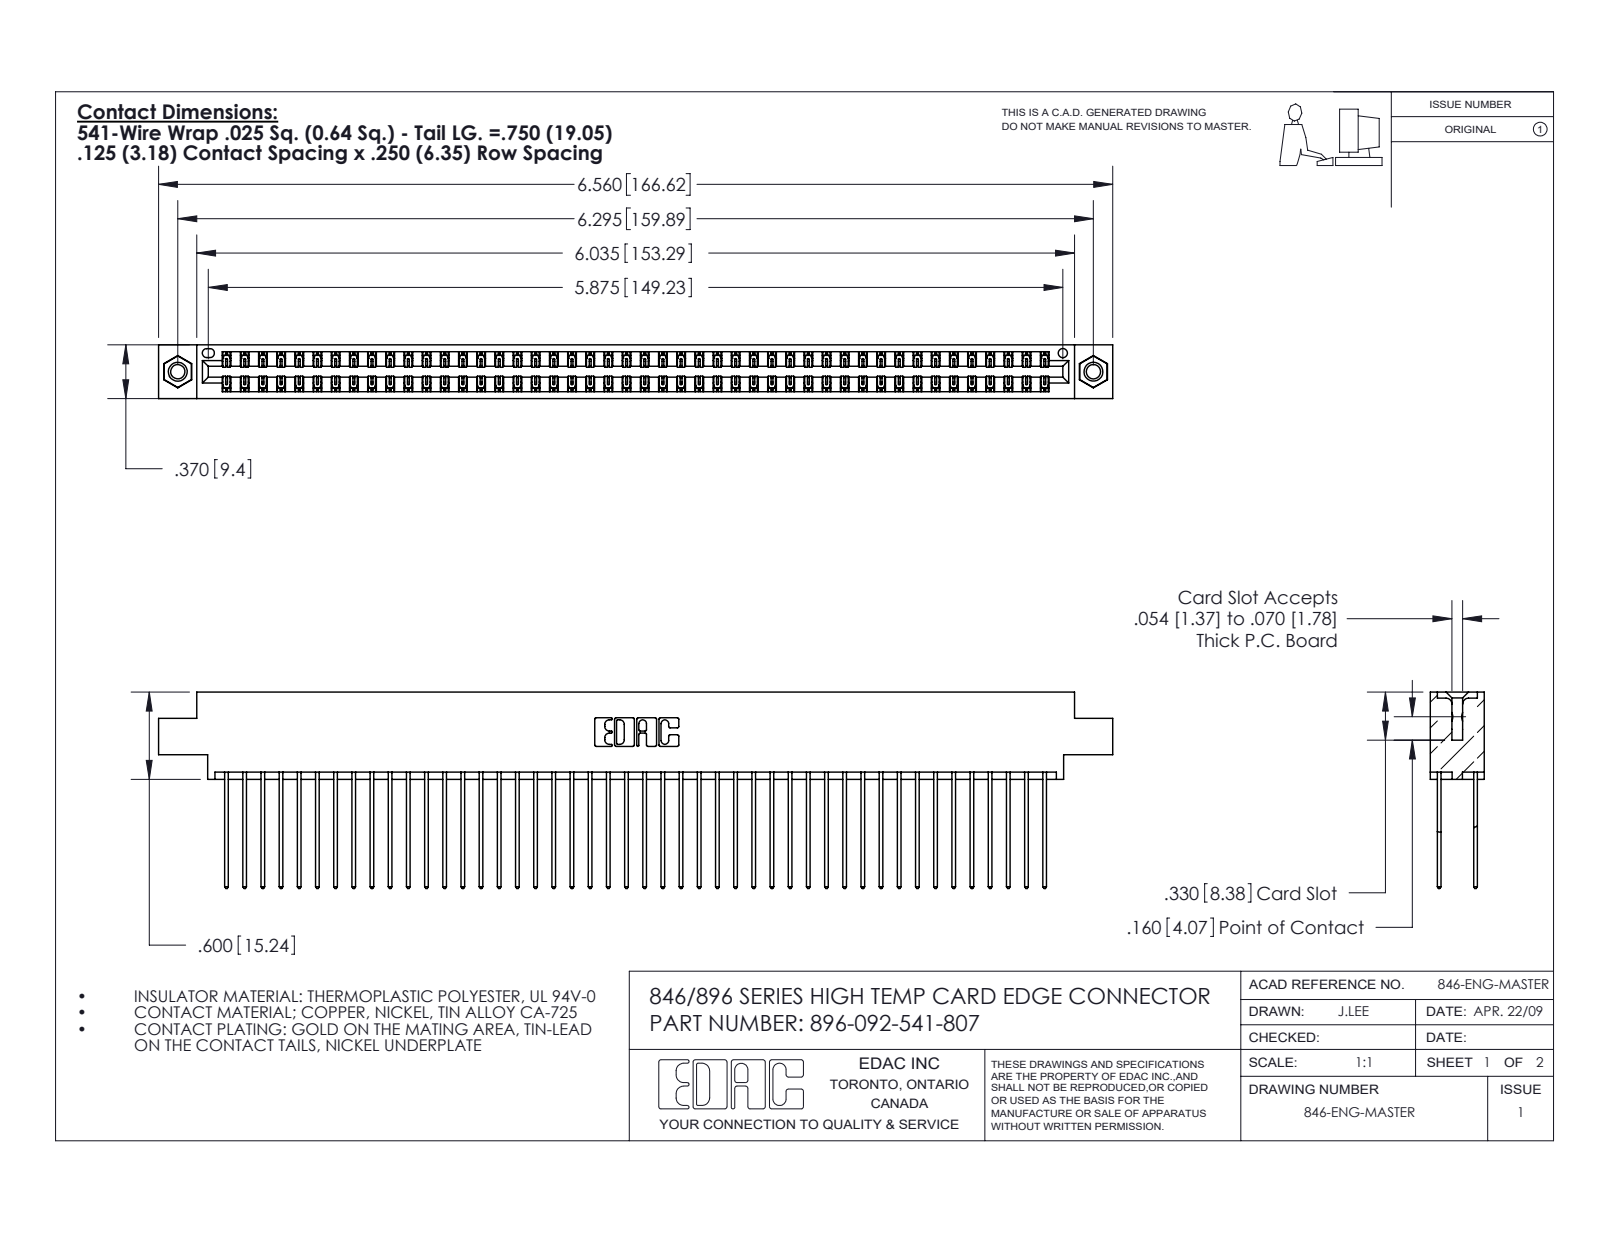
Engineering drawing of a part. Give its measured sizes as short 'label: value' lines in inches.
name: 346 Part_0.170 Offset - 0.156 Dia-TI; 345-250-001_345-250-005-103; 345-292-001_345-293-141; 396-092-541-807
written by: SolidWorks 2016 (CONFIG_CONTROL_DESIGN)
unit: in
bodies: 95 solids, 4970 faces (3332 planar, 1622 cylindrical, 16 other)
size: 6.56 × 1.35 × 0.37
volume: 1.015 in³; area: 39.8 in²
holes: 2× ⌀0.098, 2× ⌀0.125, 2× ⌀0.156, 1× ⌀0.064
bosses: 2× ⌀0.155
rounds: 138× R0.006, 92× R0.01, 22× R0.01, 6× R0.007, 6× R0.031, 3× R0.026, 2× R0.014, 2× R0.022
face distances: 0.048, 0.322, 0.25, 0.072, 0.298, 0.025, 0.37, 0.275, 0.225, 0.222
hole spacings: 0.246, 6.086, 6.295
